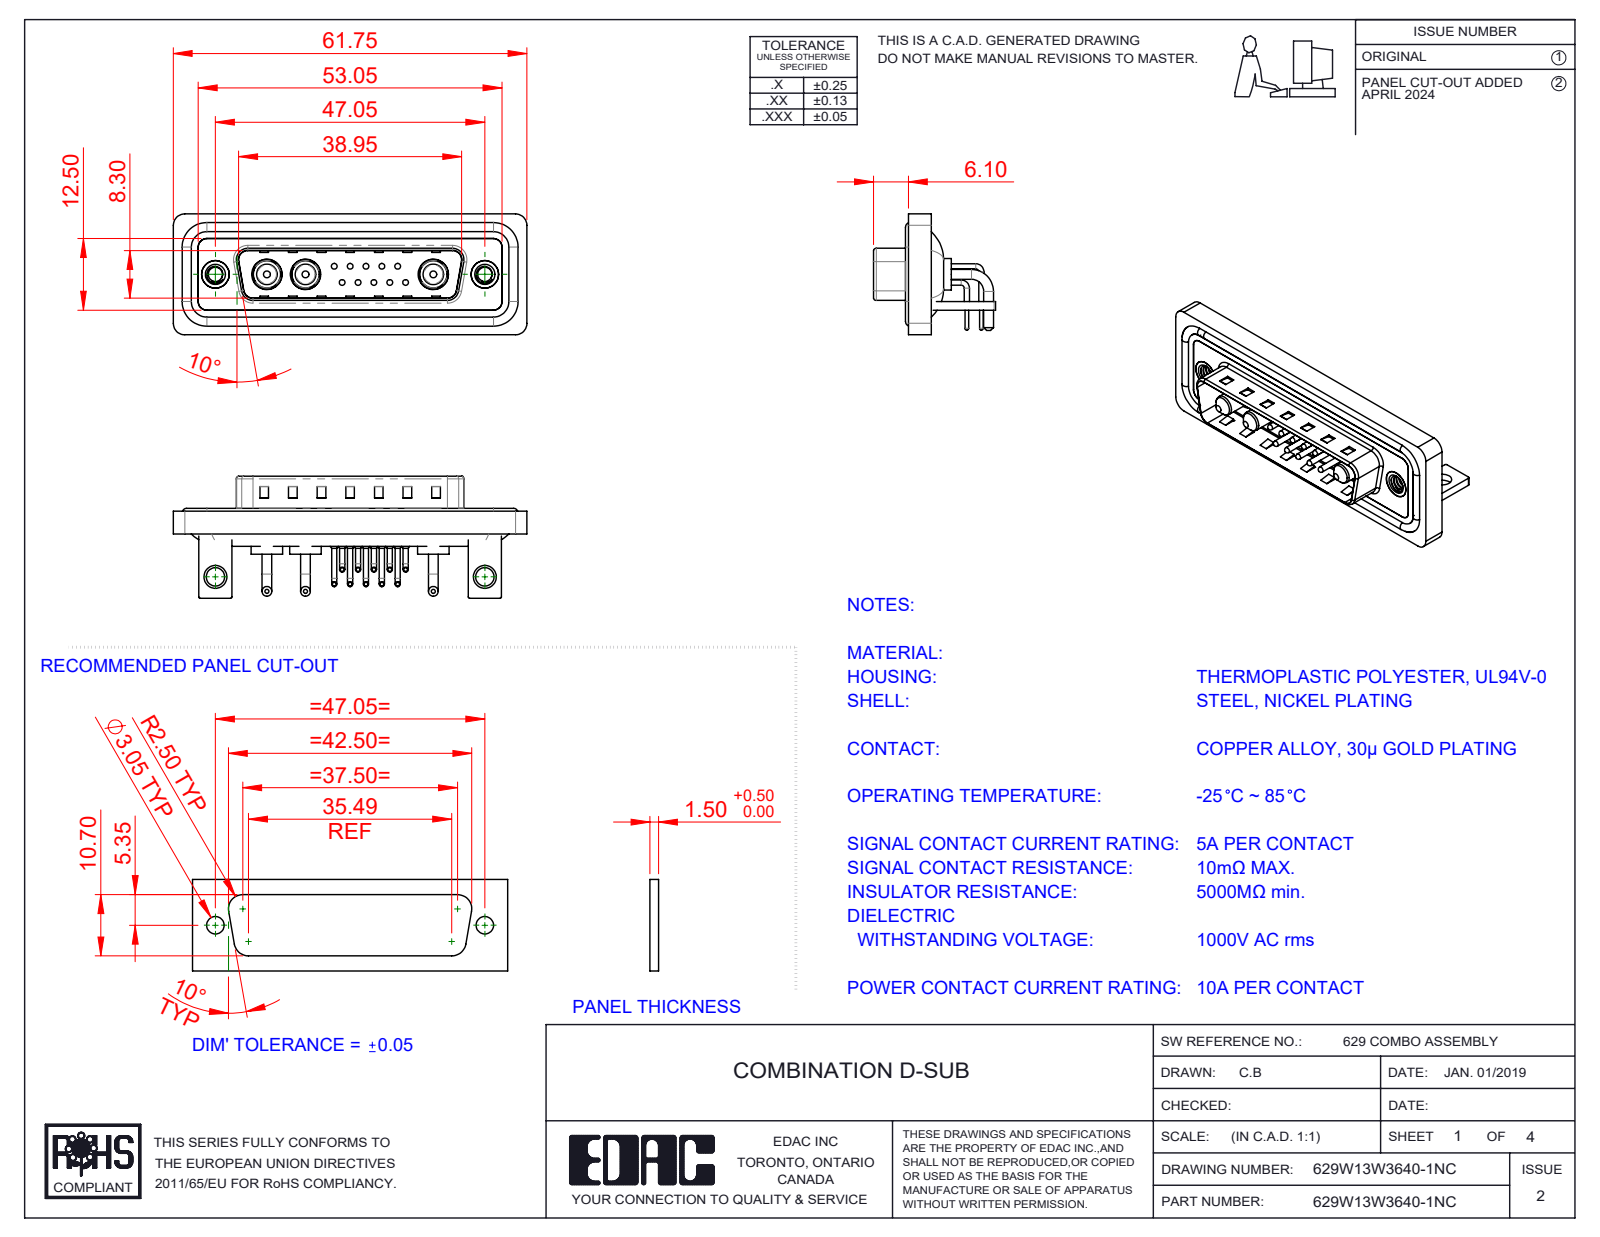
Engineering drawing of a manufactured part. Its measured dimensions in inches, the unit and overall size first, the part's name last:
Units: inches
Overall size (bounding box): 2.431 × 0.839 × 0.831
Round holes (diameter × count): ⌀0.03 ×10, ⌀0.063 ×10, ⌀0.079 ×10, ⌀0.191 ×3, ⌀0.209 ×3, ⌀0.098 ×2, ⌀0.126 ×2, ⌀0.157 ×2, ⌀0.189 ×2, ⌀0.197 ×2
Round bosses / shafts (diameter × count): ⌀0.035 ×20, ⌀0.059 ×10, ⌀0.039 ×10, ⌀0.026 ×10, ⌀0.067 ×6, ⌀0.063 ×4, ⌀0.217 ×3, ⌀0.205 ×3
Partial cylindrical surfaces — rounded edges, fillets, slot ends (radius × count): R0.079 ×19, R0.059 ×18, R0.01 ×16, R0.04 ×10, R0.02 ×9, R0.063 ×8, R0.024 ×4, R0.026 ×4
Main face-to-face distances: 0.016, 0.059, 0.031, 0.114, 0.083, 0.043, 0.161, 0.063, 0.146, 0.177
Hole centre spacings: 0.124, 0.109, 0.198, 0.218, 0.295, 0.198, 0.327, 0.398
Volume: 0.47 in³ · Surface area: 20.04 in²
Bodies: 25 solids, 1750 faces (899 planar, 629 cylindrical, 222 other)
Part name (STEP PRODUCT): 629Combo Shell Rear_25 Contacts; 629Combo Contact Row 1; 629Combo Contact Row 2; 629Combo Waterproof Housing_25 Contacts (+6 more)
STEP written by: SolidWorks 2023 (CONFIG_CONTROL_DESIGN)
